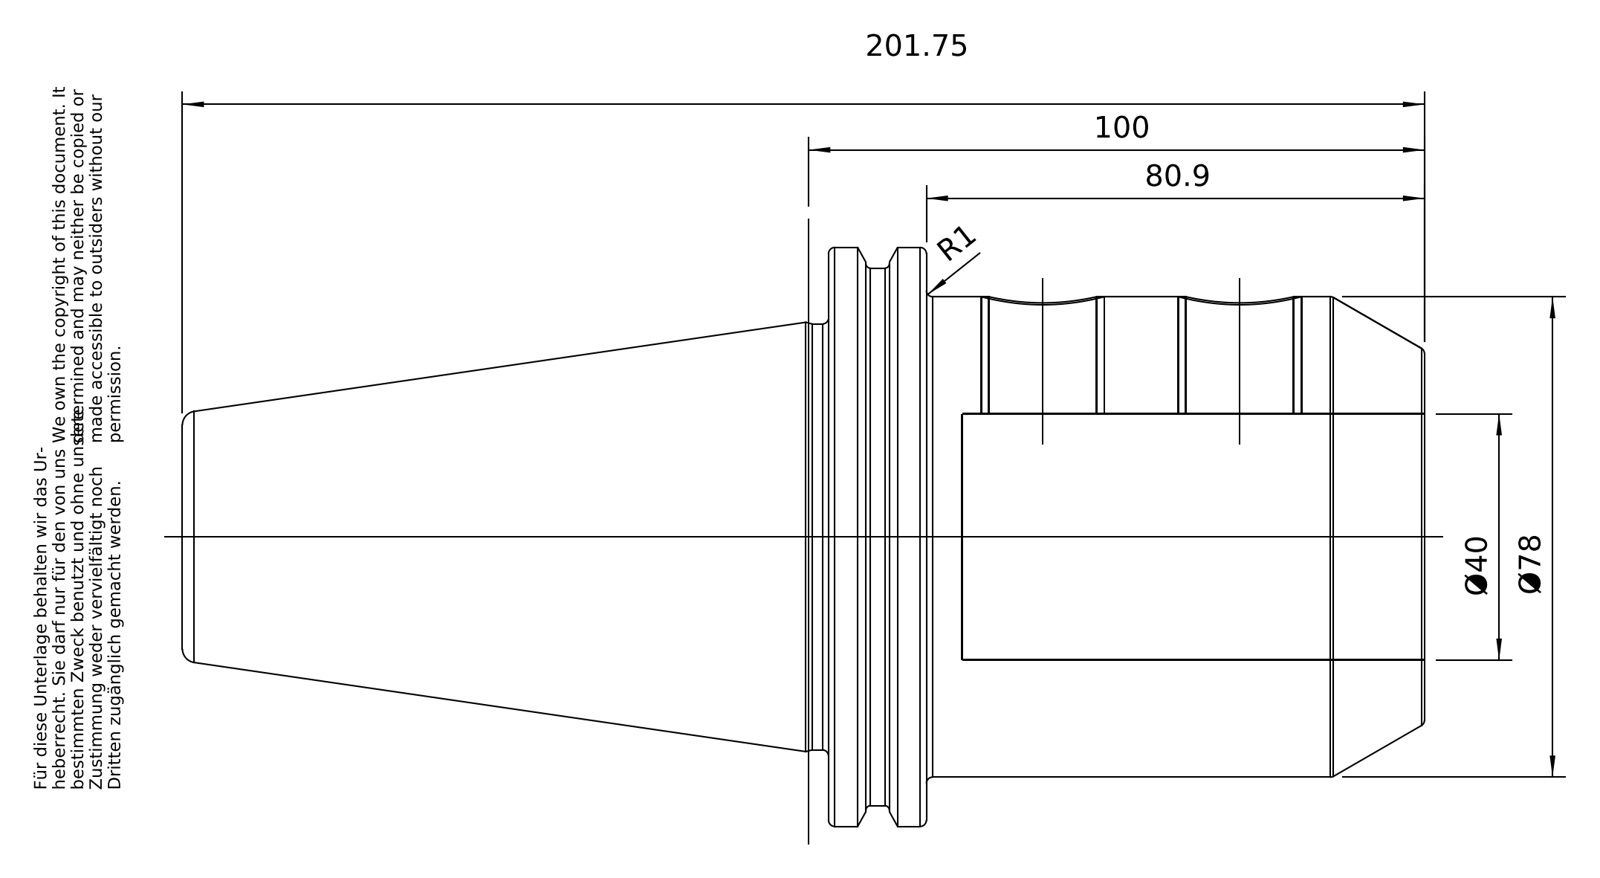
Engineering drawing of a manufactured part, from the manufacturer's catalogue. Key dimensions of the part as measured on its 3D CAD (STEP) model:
Part name (STEP PRODUCT): 50-300-40
STEP written by: PRO/ENGINEER BY PARAMETRIC TECHNOLOGY CORPORATION, 2010430 (CONFIG_CONTROL_DESIGN)
Units: millimetres
Bodies: 1 solid, 110 faces (25 planar, 36 cylindrical, 49 other)
Overall size (bounding box): 201.6 × 97.47 × 94
Volume: 606 843 mm³ · Surface area: 73 759 mm²
Round holes (diameter × count): ⌀17.5 ×2, ⌀20 ×2, ⌀20.75 ×1, ⌀25.01 ×1, ⌀25.7 ×1, ⌀40 ×1
Round bosses / shafts (diameter × count): ⌀91 ×1, ⌀78 ×1, ⌀69.15 ×1, ⌀24.01 ×1
Partial cylindrical surfaces — rounded edges, fillets, slot ends (radius × count): R1.75 ×5, R48.74 ×1
Main face-to-face distances: 15.85, 96.8, 80.95, 21.7, 5.85, 75.1, 104.8, 120.65, 126.5, 201.6
Hole centre spacings: 32
